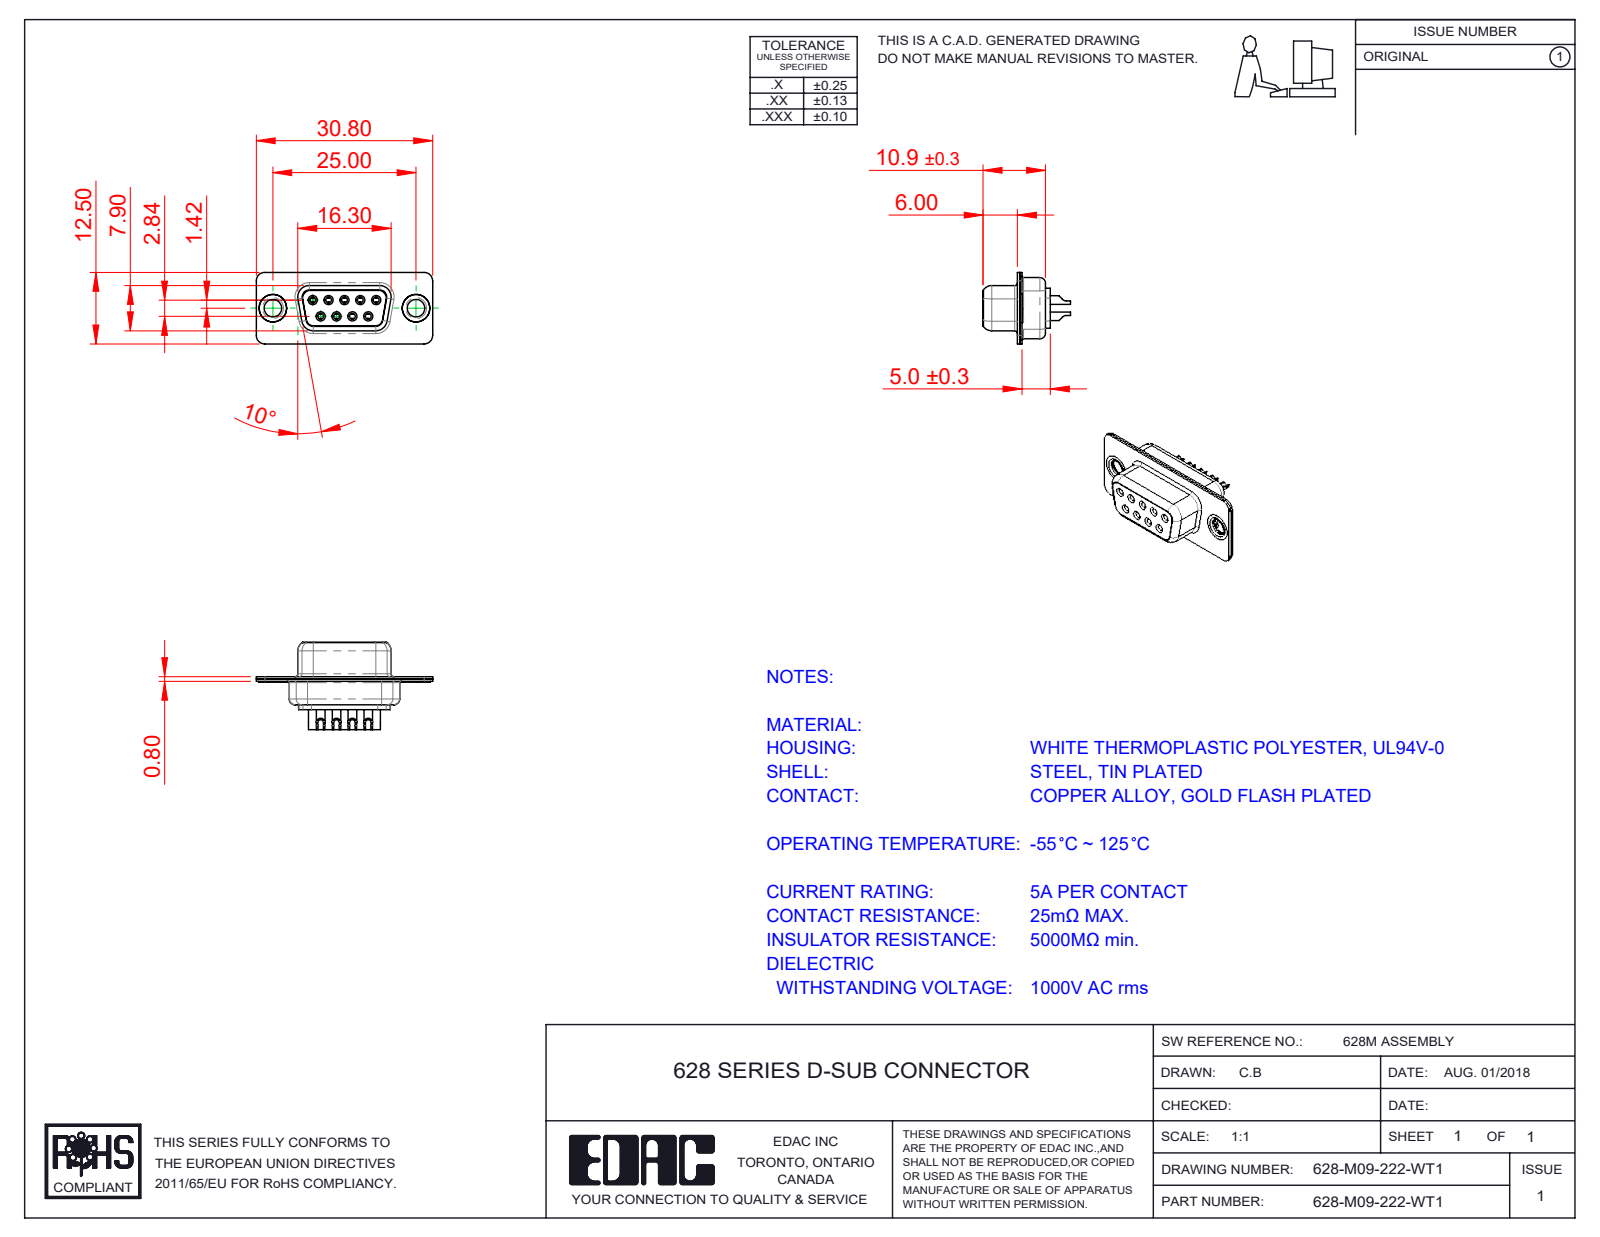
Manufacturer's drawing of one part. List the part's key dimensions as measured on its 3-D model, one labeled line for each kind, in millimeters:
Part name (STEP PRODUCT): 628M Contact Row 1_22; 628M Thru Hole Rivet; 628-M09-222-WT1; 628M Shell Rear_09 Contacts (+3 more)
STEP written by: SolidWorks 2020 (CONFIG_CONTROL_DESIGN)
Units: millimetres
Bodies: 14 solids, 749 faces (221 planar, 310 cylindrical, 218 other)
Overall size (bounding box): 30.8 × 15.25 × 12.5
Volume: 1 637 mm³ · Surface area: 4 355 mm²
Round holes (diameter × count): ⌀1 ×9, ⌀1.1 ×9, ⌀1.7 ×9, ⌀1.8 ×9, ⌀2 ×9, ⌀3.05 ×2, ⌀4 ×2, ⌀4.8 ×2
Round bosses / shafts (diameter × count): ⌀2.2 ×9, ⌀1.6 ×9, ⌀1.5 ×9, ⌀5 ×2, ⌀4.9 ×2, ⌀3.55 ×2
Partial cylindrical surfaces — rounded edges, fillets, slot ends (radius × count): R1.5 ×16, R2 ×12, R1.35 ×8, R1.6 ×8, R1 ×6, R0.25 ×4, R0.5 ×4, R0.6 ×4
Main face-to-face distances: 0.4, 1.4, 0.45, 8.45, 0.8, 8.9, 1.8, 7.05, 1, 0.85
Hole centre spacings: 3.16, 2.77, 5.54, 5.03, 5.04, 8.31, 7.1, 7.48
